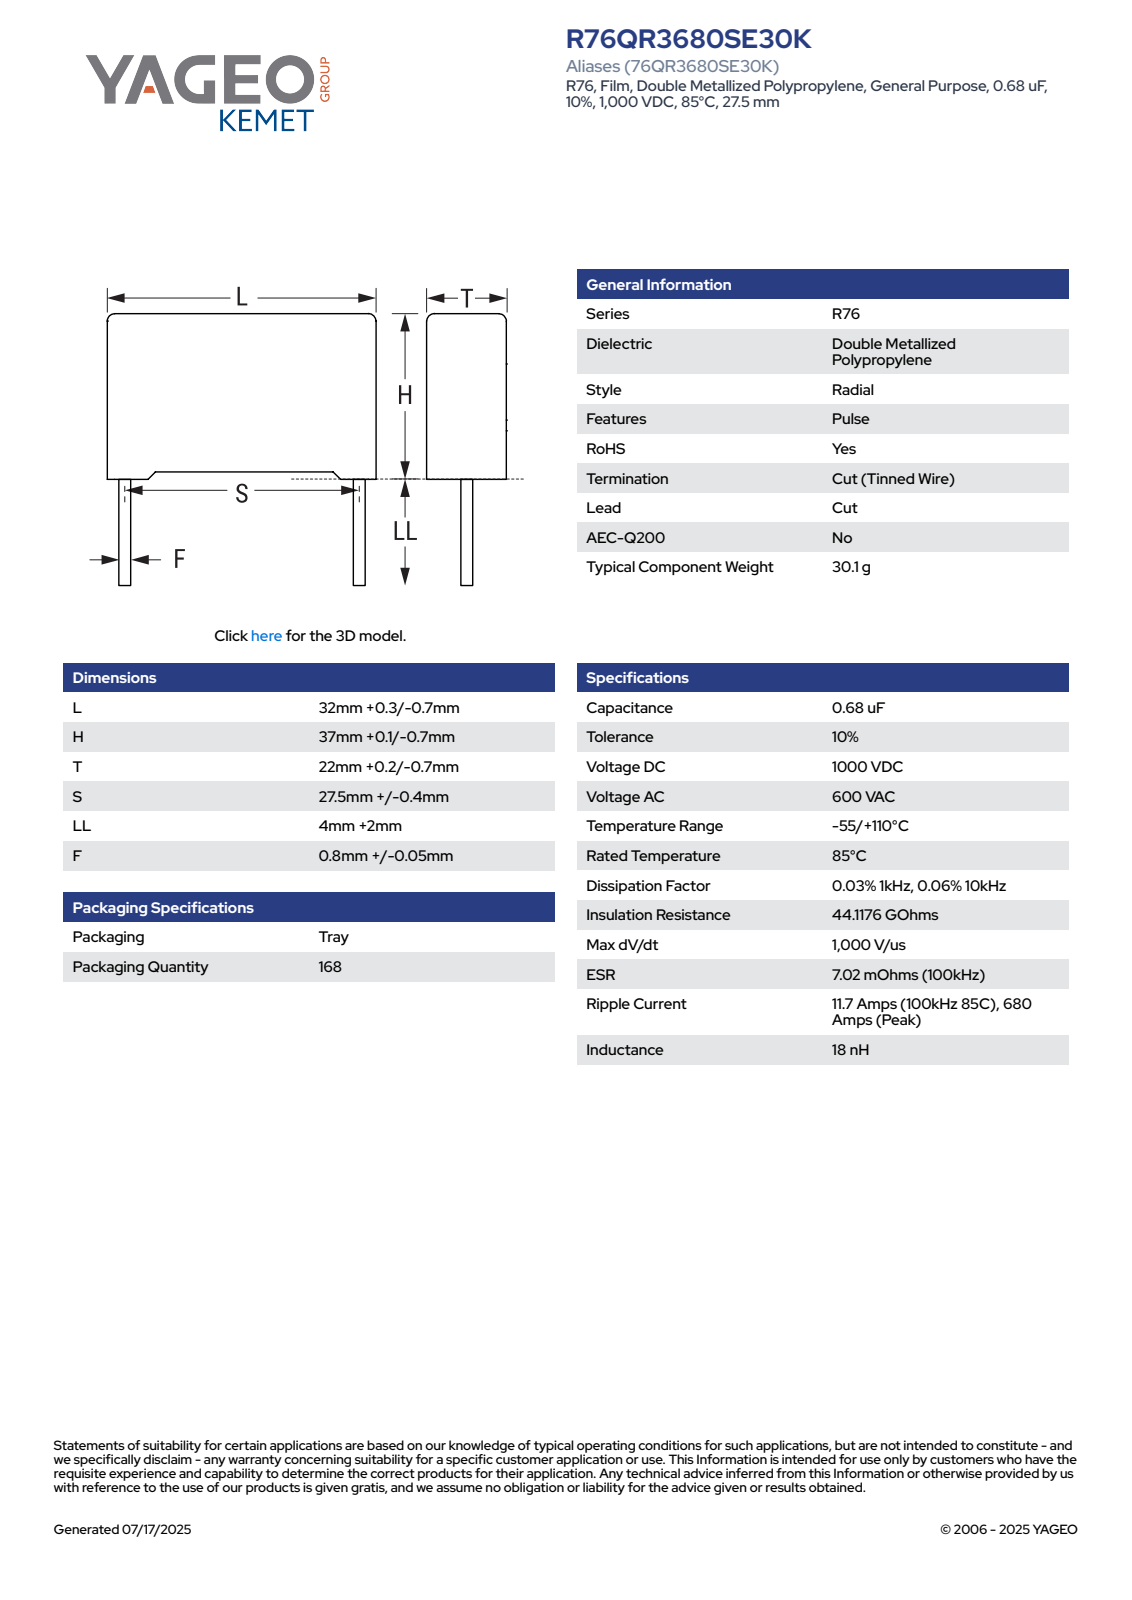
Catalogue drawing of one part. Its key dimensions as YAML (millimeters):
part_name: "CFR_RB2_32X37X22_L32.3H37.1T22.2S27.5LL6F0.85"
step_written_by: "SolidWorks 2021 (AUTOMOTIVE_DESIGN)"
units: millimeters
bodies: {solids: 4, faces: 85, planar: 77, cylindrical: 8, other: 0}
overall_size: [43.1, 32.3, 22.2]
volume: 25842
surface_area: 5562
round_bosses_or_shafts:
  - {diameter: 0.85, count: 2}
partial_cylinders:
  - {radius: 0.5, count: 4}
face_to_face_distances: [22.2, 32.3, 35.82, 0.53, 36.35, 0.75, 1.28, 37.1, 1.08, 31.22]
